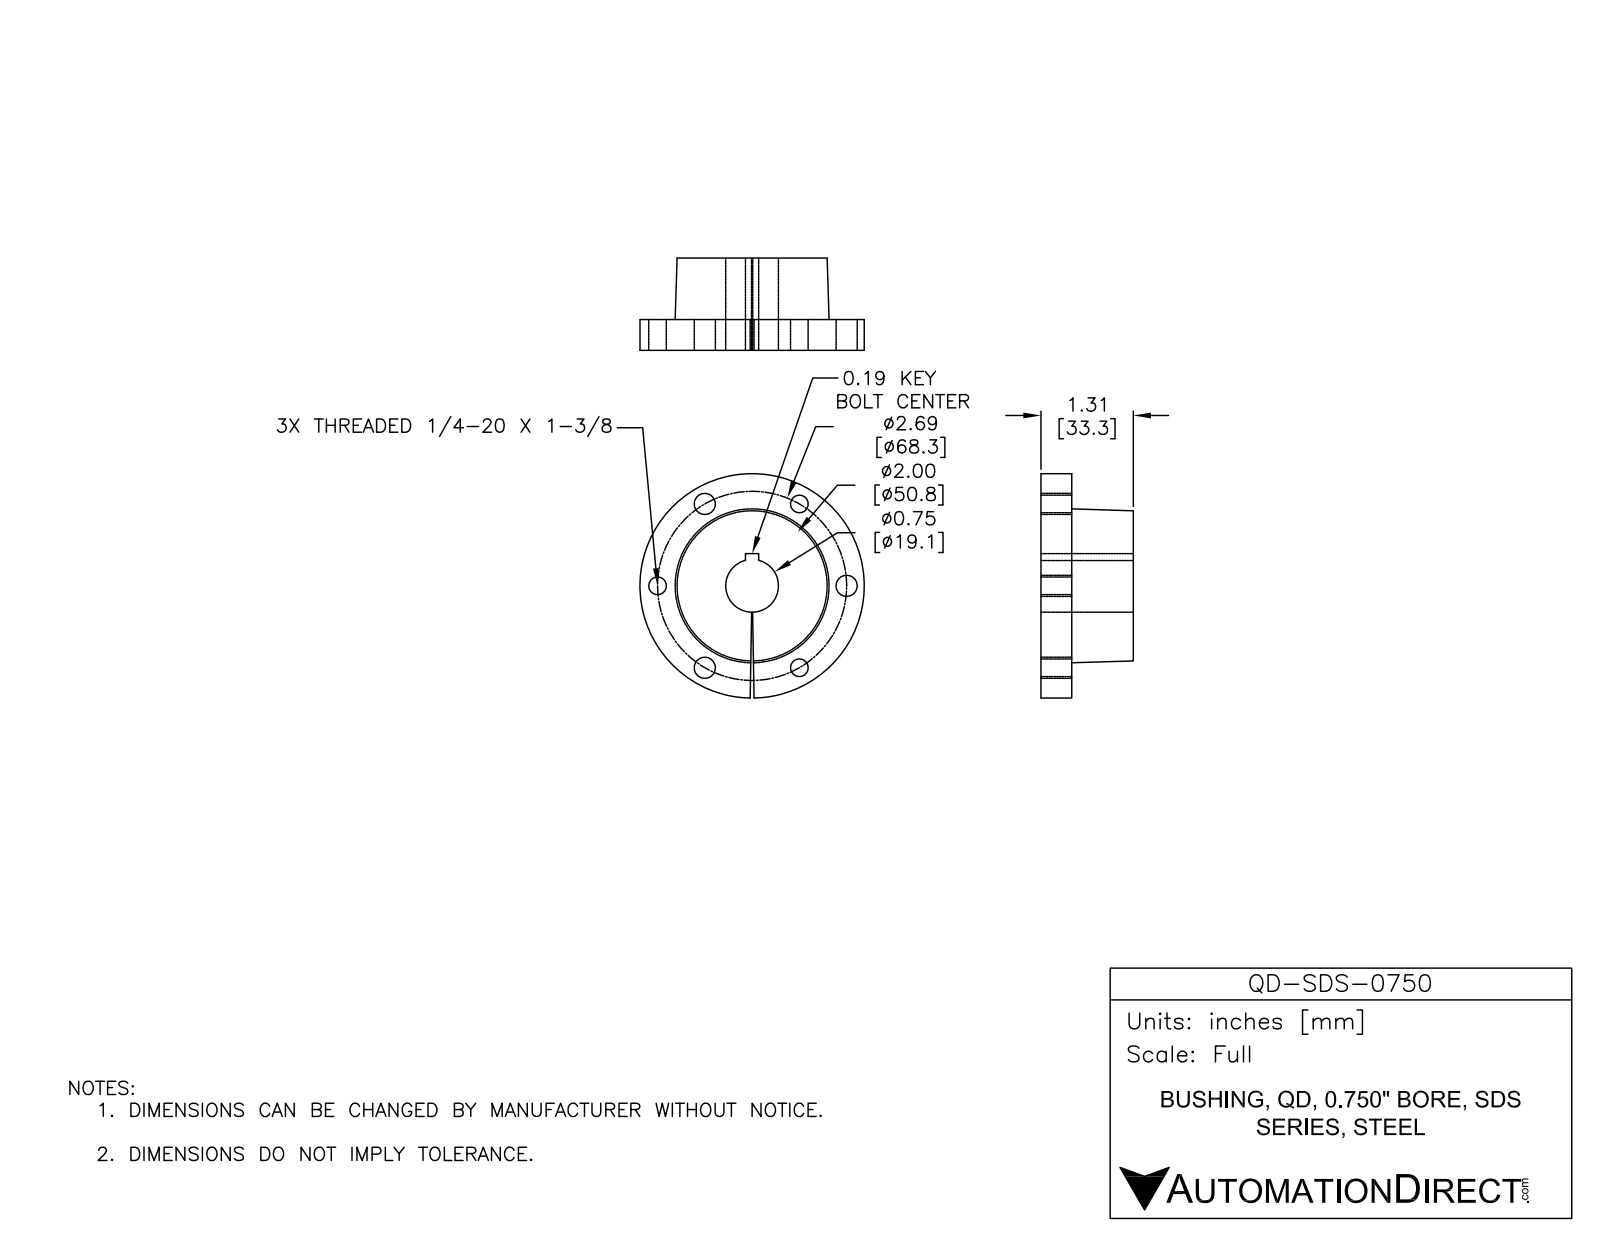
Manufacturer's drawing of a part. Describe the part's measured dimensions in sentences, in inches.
The part is named "QD-SDS-0750". Its 3-D file was written by "SolidWorks 2014 (AUTOMOTIVE_DESIGN)". It is 1 solid with 29 faces: 8 planar, 18 cylindrical and 3 other. Overall it measures 3.188 by 3.187 by 1.313 inches. Its volume is 5.903 cubic inches and its surface area 32.24 square inches. Round holes: 3 of diameter 0.25, 3 of diameter 0.3, 1 of diameter 0.75. Round bosses or shafts: 1 of diameter 3.187. The main face-to-face distances are 0.437, 1.313, 0.875, 0.187. The hole center spacings are 1.344, 2.328, 1.344, 2.688, 2.687.
